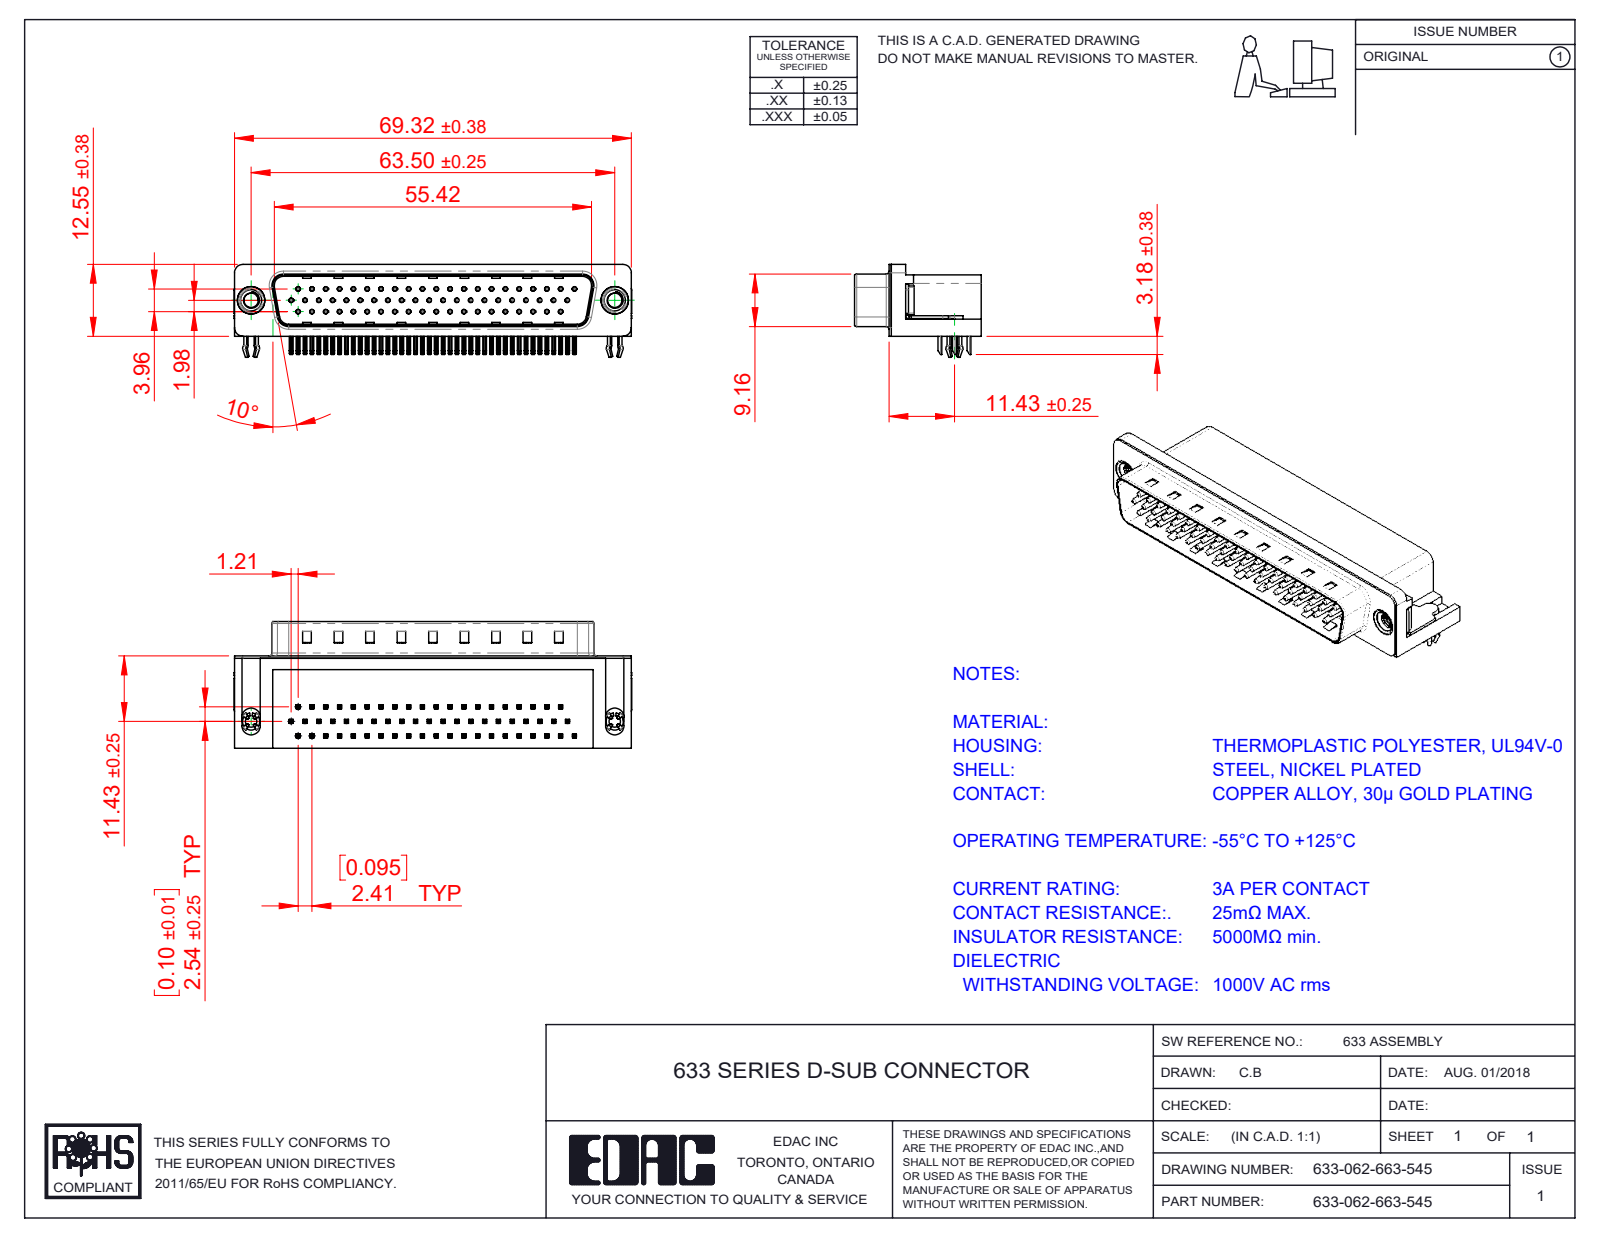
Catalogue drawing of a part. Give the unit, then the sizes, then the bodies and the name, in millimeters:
Units: millimetres
Overall size (bounding box): 69.4 × 22.1 × 16.25
Round holes (diameter × count): ⌀0.35 ×62, ⌀0.8 ×62, ⌀2 ×2, ⌀2.5 ×2, ⌀4 ×2, ⌀4.8 ×2, ⌀5 ×2
Round bosses / shafts (diameter × count): ⌀0.75 ×62, ⌀4.9 ×2, ⌀4.75 ×2, ⌀3.9 ×2, ⌀3 ×2
Partial cylindrical surfaces — rounded edges, fillets, slot ends (radius × count): R0.25 ×260, R0.12 ×124, R1 ×16, R0.5 ×9, R1.6 ×8, R1.5 ×7, R0.9 ×4, R2 ×4
Main face-to-face distances: 0.4, 10.35, 15.7, 8.76, 2.9, 2.5, 2.54, 8.36, 2.1, 16.1
Hole centre spacings: 2.41, 4.82, 7.24, 9.65, 14.48, 16.89, 4.83, 7.23
Volume: 11 059 mm³ · Surface area: 13 483 mm²
Bodies: 68 solids, 5196 faces (3255 planar, 1452 cylindrical, 489 other)
Part name (STEP PRODUCT): 633-062-663-545; 633 M3 Threaded Rivet; 633 Housing_62 Contact; 633 Shell_62 Contact (+4 more)
STEP written by: SolidWorks 2016 (CONFIG_CONTROL_DESIGN)
